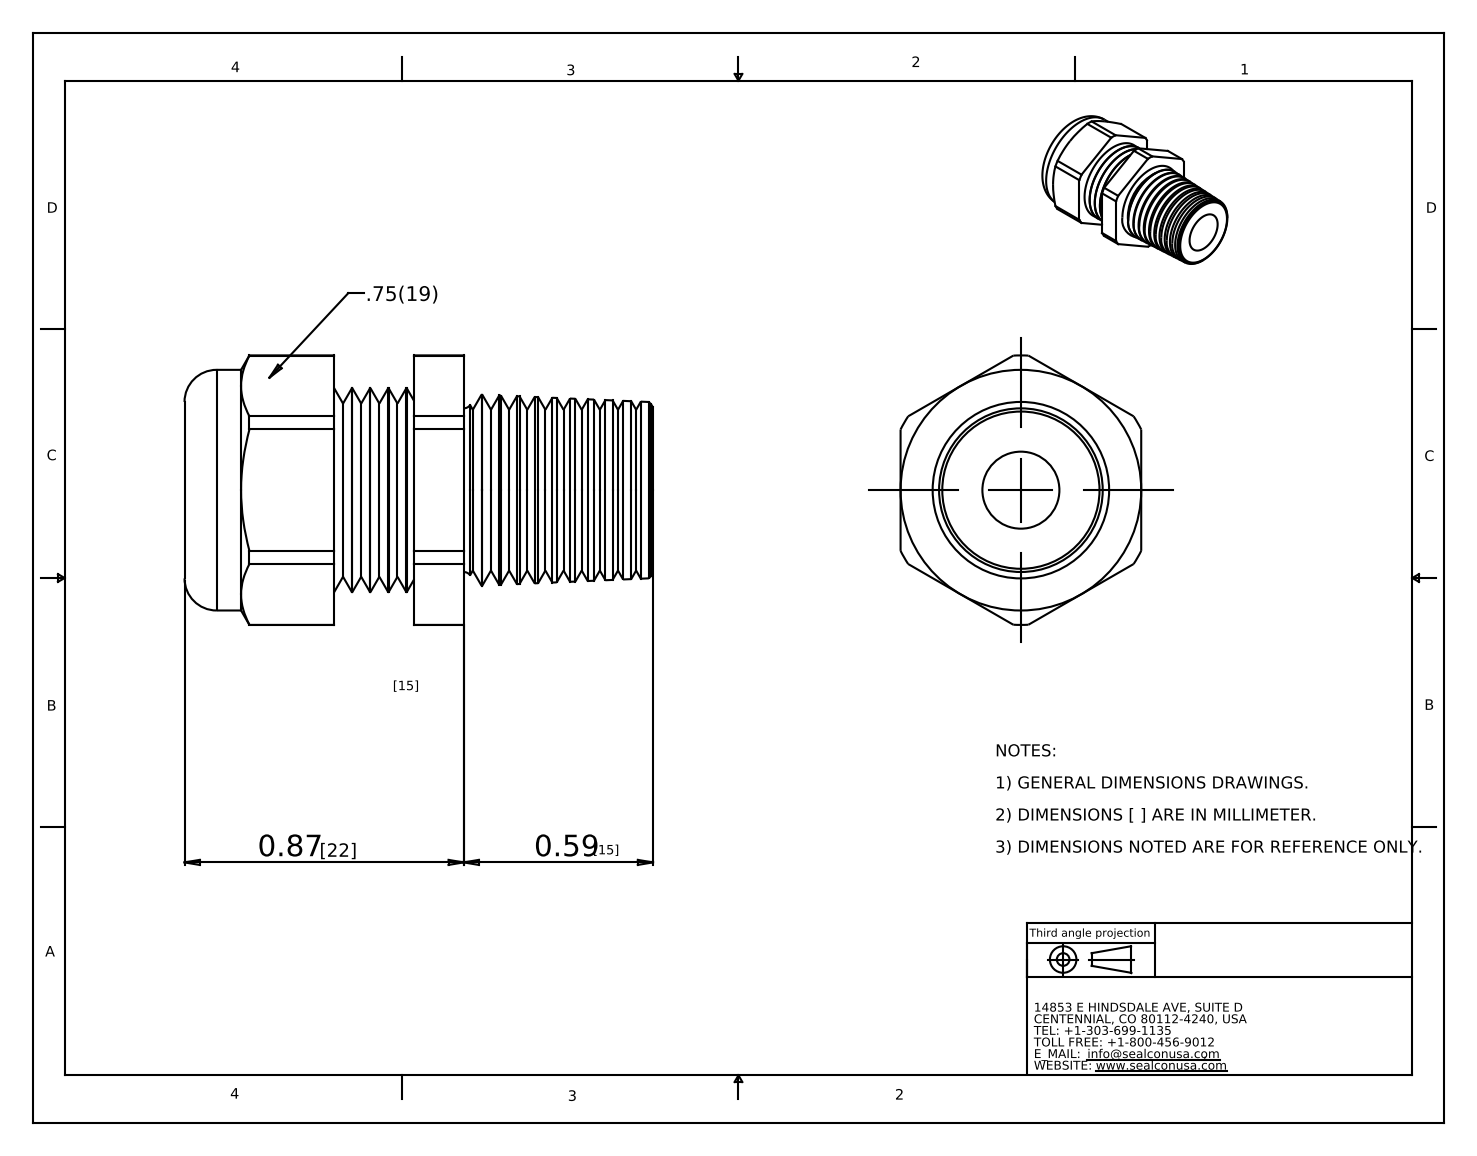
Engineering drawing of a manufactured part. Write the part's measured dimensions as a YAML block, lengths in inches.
part_name: "CD09NR-BK"
step_written_by: "SolidWorks 2009 (CONFIG_CONTROL_DESIGN)"
units: inches
bodies: {solids: 2, faces: 152, planar: 20, cylindrical: 32, other: 100}
overall_size: [1.46, 0.84, 0.75]
volume: 0.407
surface_area: 7.52
round_holes:
  - {diameter: 0.24, count: 1}
  - {diameter: 0.51, count: 1}
round_bosses_or_shafts:
  - {diameter: 0.75, count: 1}
  - {diameter: 0.636, count: 1}
partial_cylinders:
  - {radius: 0.42, count: 1}
face_to_face_distances: [0.75, 0.694, 0.539, 0.154, 0.29, 0.25, 0.404, 0.156, 0.446, 0.696]
